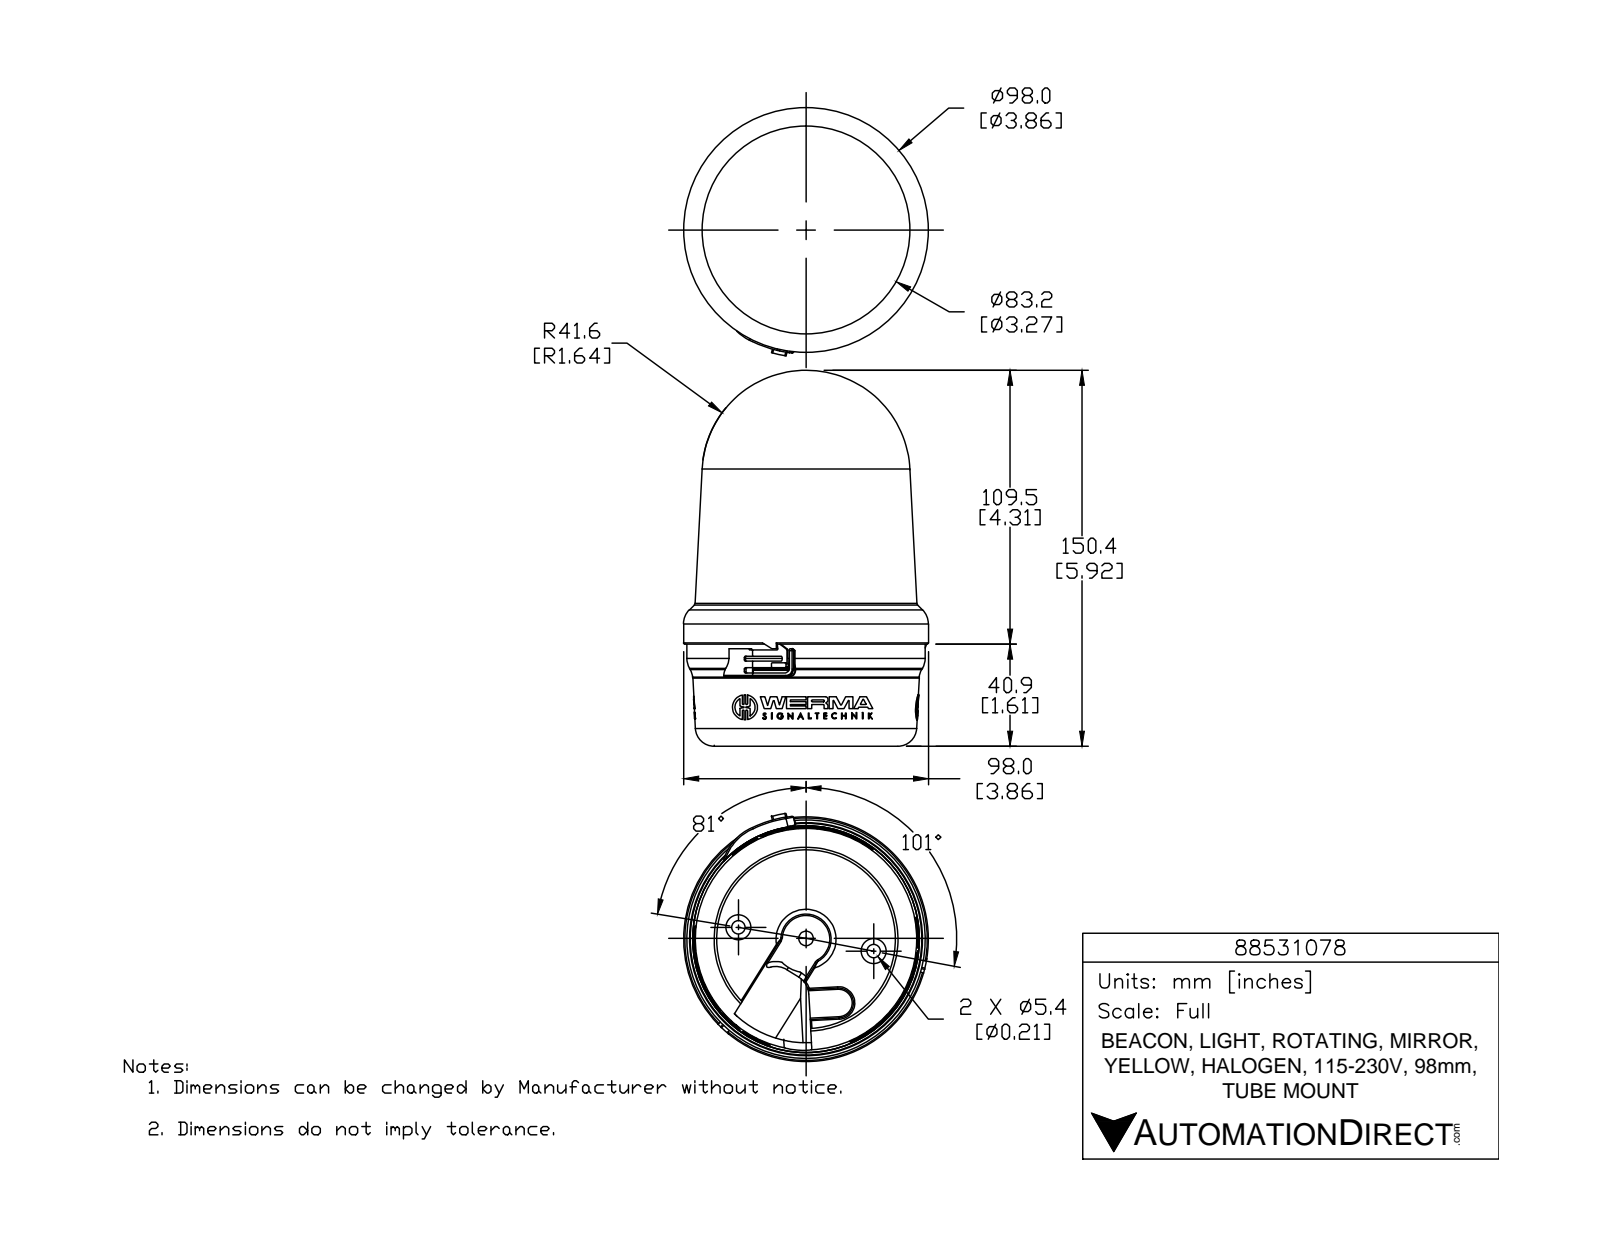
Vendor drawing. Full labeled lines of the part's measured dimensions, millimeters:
Part name (STEP PRODUCT): 88531078
STEP written by: SolidWorks 2015 (AUTOMOTIVE_DESIGN)
Units: millimetres
Bodies: 1 solid, 1006 faces (554 planar, 189 cylindrical, 263 other)
Overall size (bounding box): 201 × 99.4 × 98
Volume: 896 400 mm³ · Surface area: 58 960 mm²
Round holes (diameter × count): ⌀2 ×3, ⌀25.7 ×1, ⌀26 ×1
Round bosses / shafts (diameter × count): ⌀11.5 ×3, ⌀2.9 ×3, ⌀98 ×1, ⌀35.8 ×1, ⌀32 ×1
Partial cylindrical surfaces — rounded edges, fillets, slot ends (radius × count): R0.5 ×12, R0.2 ×9, R0.2 ×6, R0.4 ×6, R0.4 ×6, R0.4 ×6, R6.7 ×6, R0.2 ×3
Main face-to-face distances: 56.2, 11.7, 68, 8.5, 3.2, 64.7, 66.1, 62.9, 54.4, 1.9
